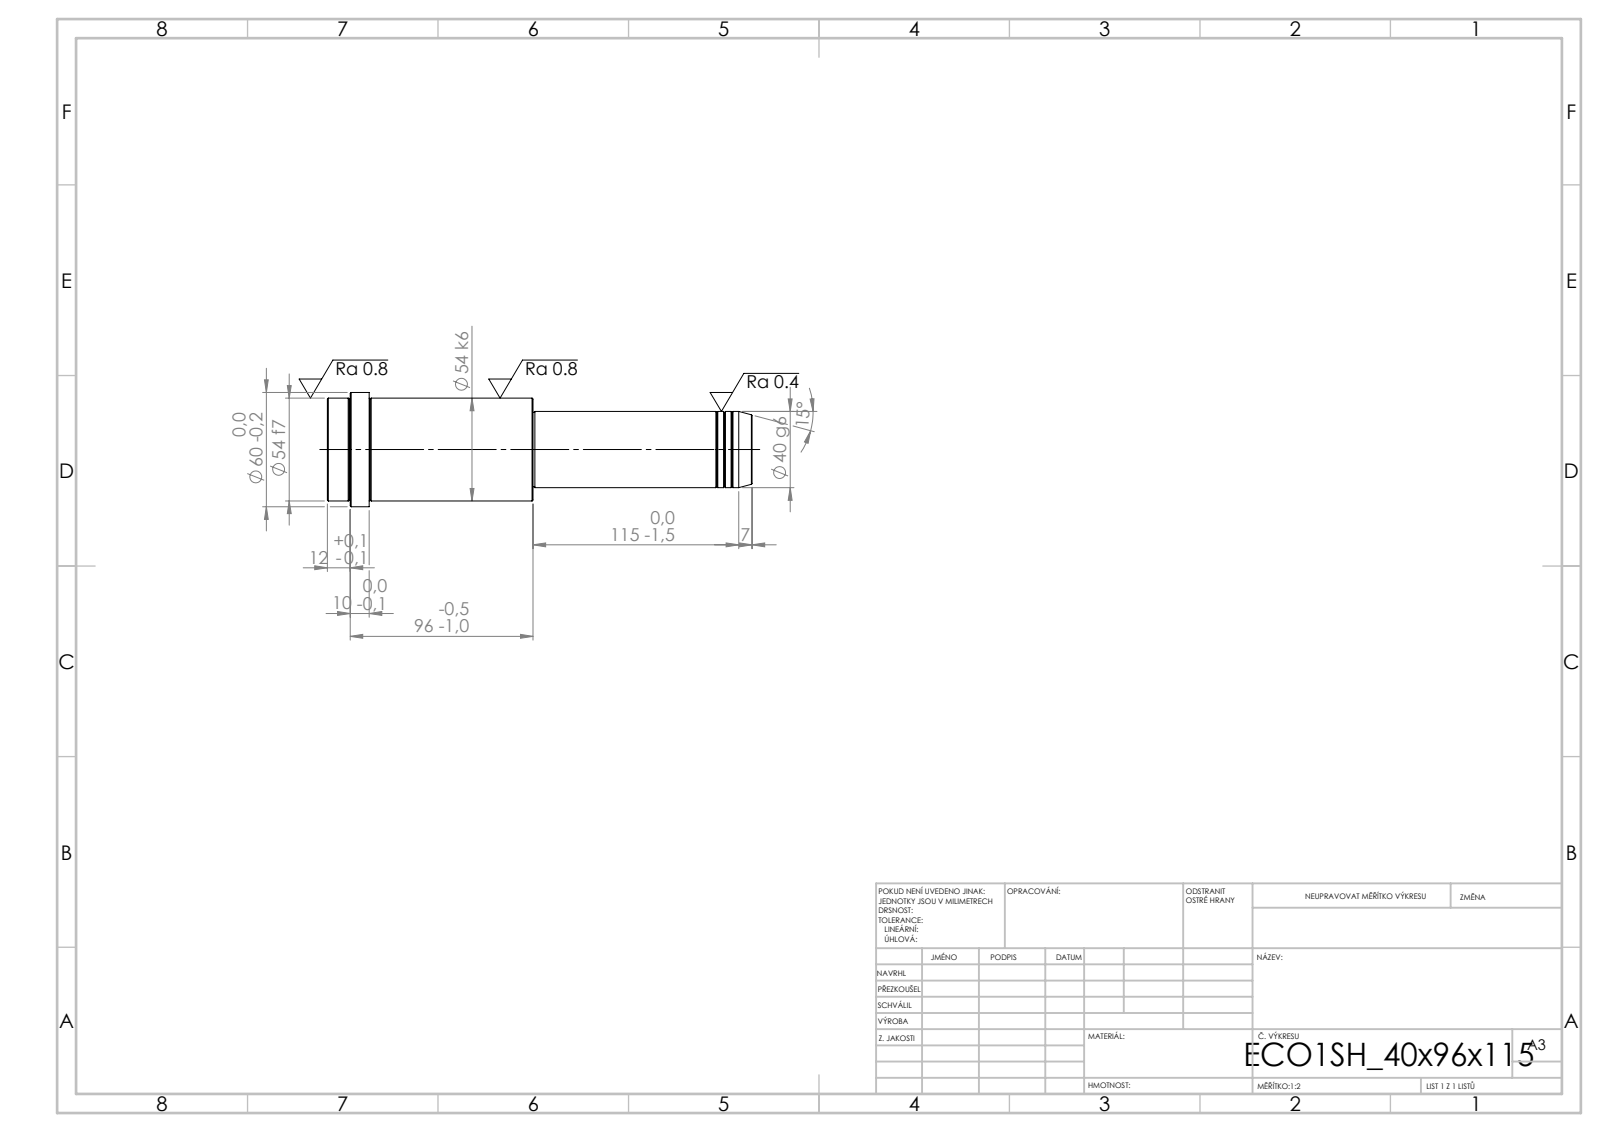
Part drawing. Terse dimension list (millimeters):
written by: SolidWorks 2019 (CONFIG_CONTROL_DESIGN)
unit: mm
bodies: 1 solid, 52 faces (6 planar, 16 cylindrical, 30 other)
size: 223 × 60 × 60
volume: 396 021 mm³; area: 38 726 mm²
bosses: 1× ⌀60, 1× ⌀54, 1× ⌀40, 1× ⌀39
face distances: 108, 115, 223, 201, 86, 22, 211, 96, 10, 12
